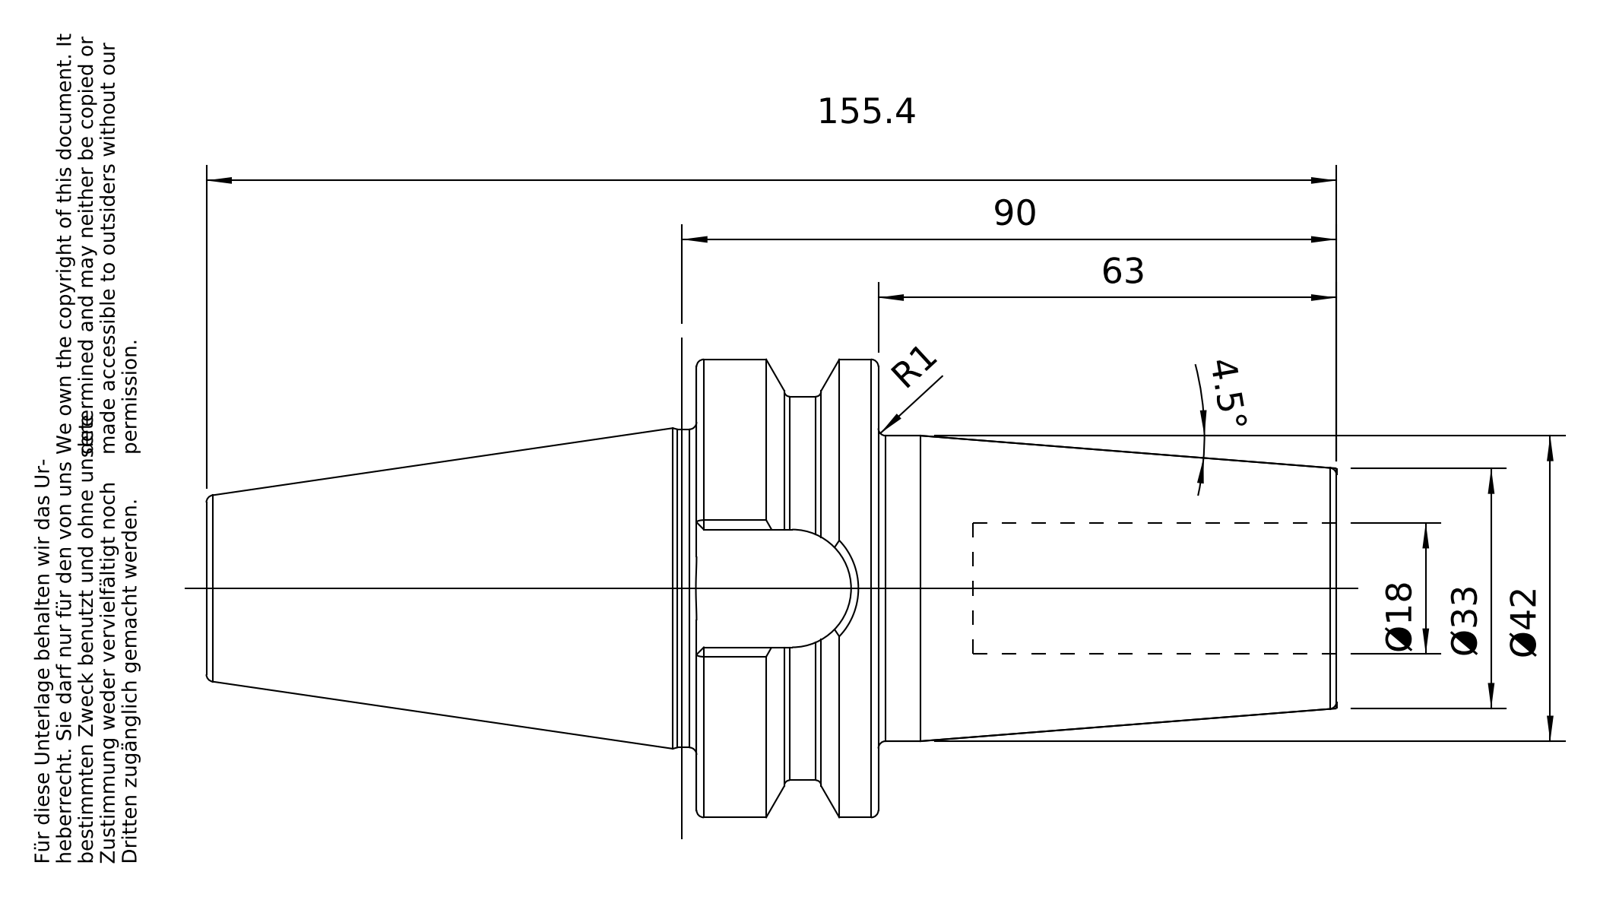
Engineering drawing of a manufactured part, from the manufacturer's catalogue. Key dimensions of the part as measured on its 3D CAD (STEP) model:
Part name (STEP PRODUCT): 40-640-18
STEP written by: PRO/ENGINEER BY PARAMETRIC TECHNOLOGY CORPORATION, 2010430 (CONFIG_CONTROL_DESIGN)
Units: millimetres
Bodies: 1 solid, 96 faces (26 planar, 22 cylindrical, 48 other)
Overall size (bounding box): 155.4 × 62.98 × 62.98
Volume: 184 949 mm³ · Surface area: 31 562 mm²
Round holes (diameter × count): ⌀13.84 ×1, ⌀17.01 ×1, ⌀17.5 ×1, ⌀18 ×1
Round bosses / shafts (diameter × count): ⌀62.98 ×1, ⌀52.75 ×1, ⌀43.75 ×1, ⌀42 ×1, ⌀16.01 ×1
Partial cylindrical surfaces — rounded edges, fillets, slot ends (radius × count): R8.1 ×1
Main face-to-face distances: 25, 88, 63, 44.9, 38, 13, 50, 16.2, 67.4, 92.4
